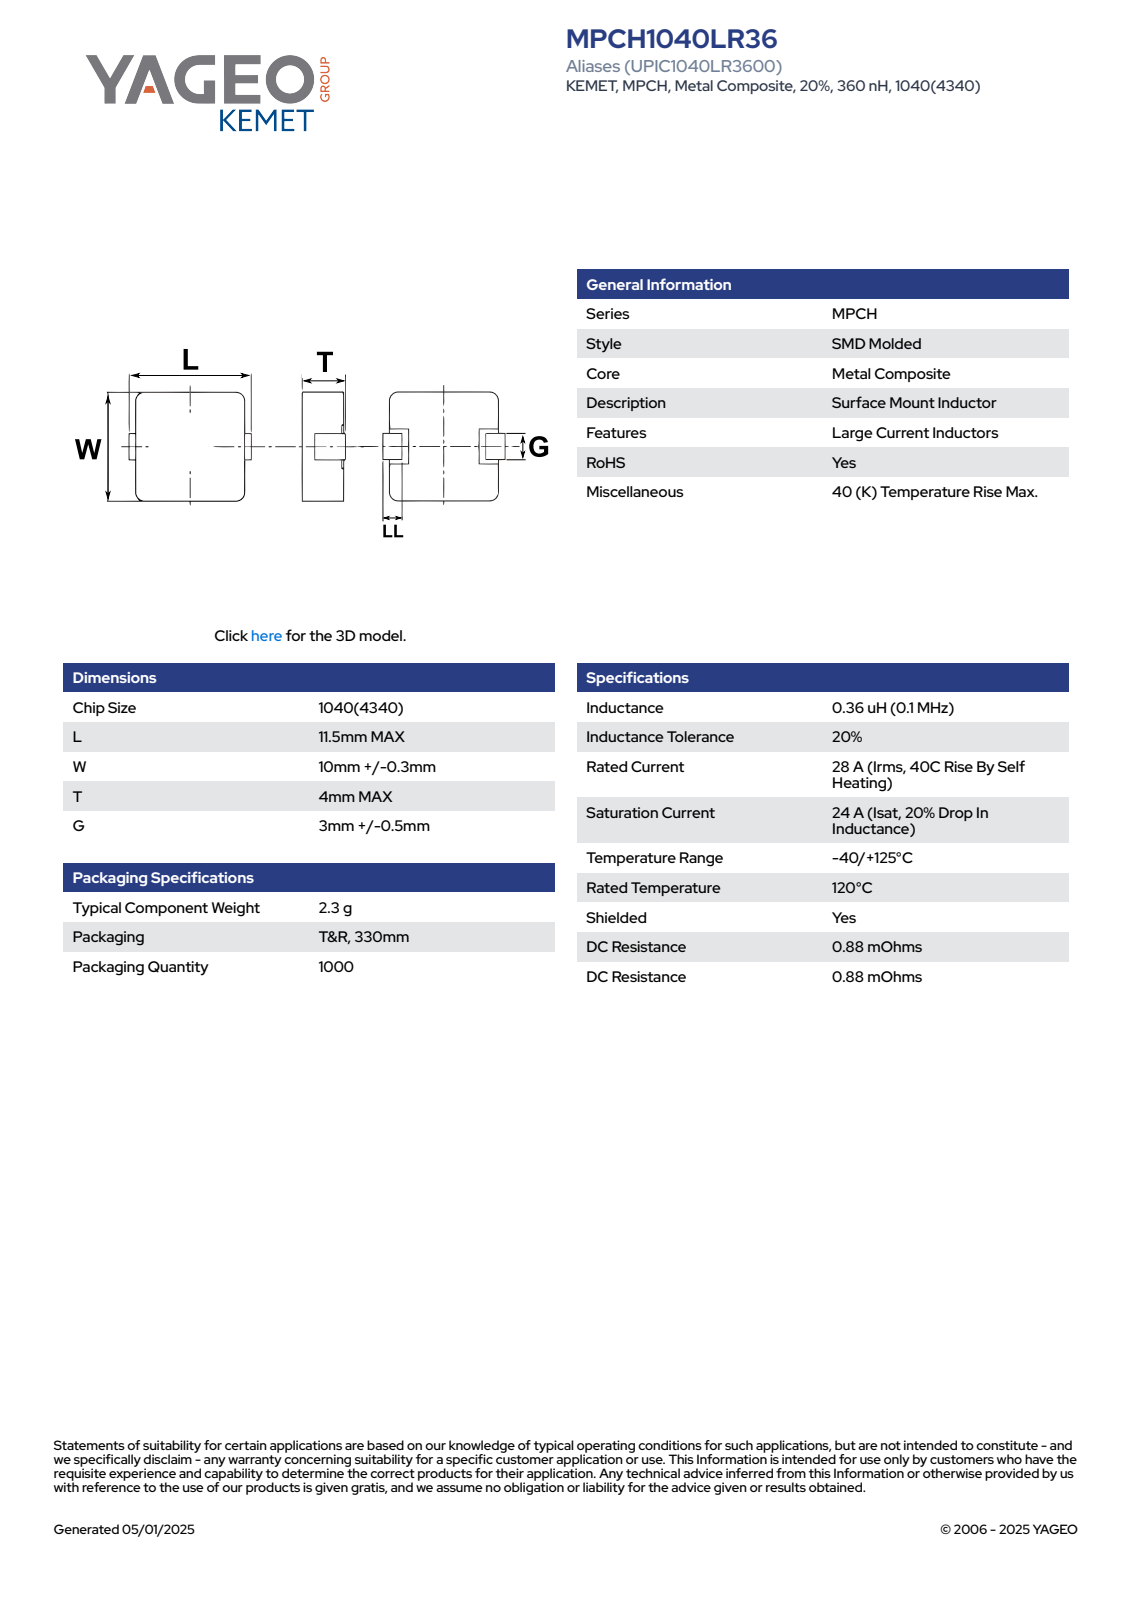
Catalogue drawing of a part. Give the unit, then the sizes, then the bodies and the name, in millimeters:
Units: millimetres
Overall size (bounding box): 11.5 × 10.3 × 4
Partial cylindrical surfaces — rounded edges, fillets, slot ends (radius × count): R0.88 ×4
Main face-to-face distances: 3.95, 10.3, 11.09, 11.3, 11.1, 11.29, 11.08, 11.4, 11.19, 11.2
Volume: 451 mm³ · Surface area: 443 mm²
Bodies: 4 solids, 105 faces (93 planar, 12 cylindrical, 0 other)
Part name (STEP PRODUCT): IS_MPC_4539_L11.5W10.3T4LL2.1G3.5
STEP written by: SolidWorks 2014 (AUTOMOTIVE_DESIGN)
